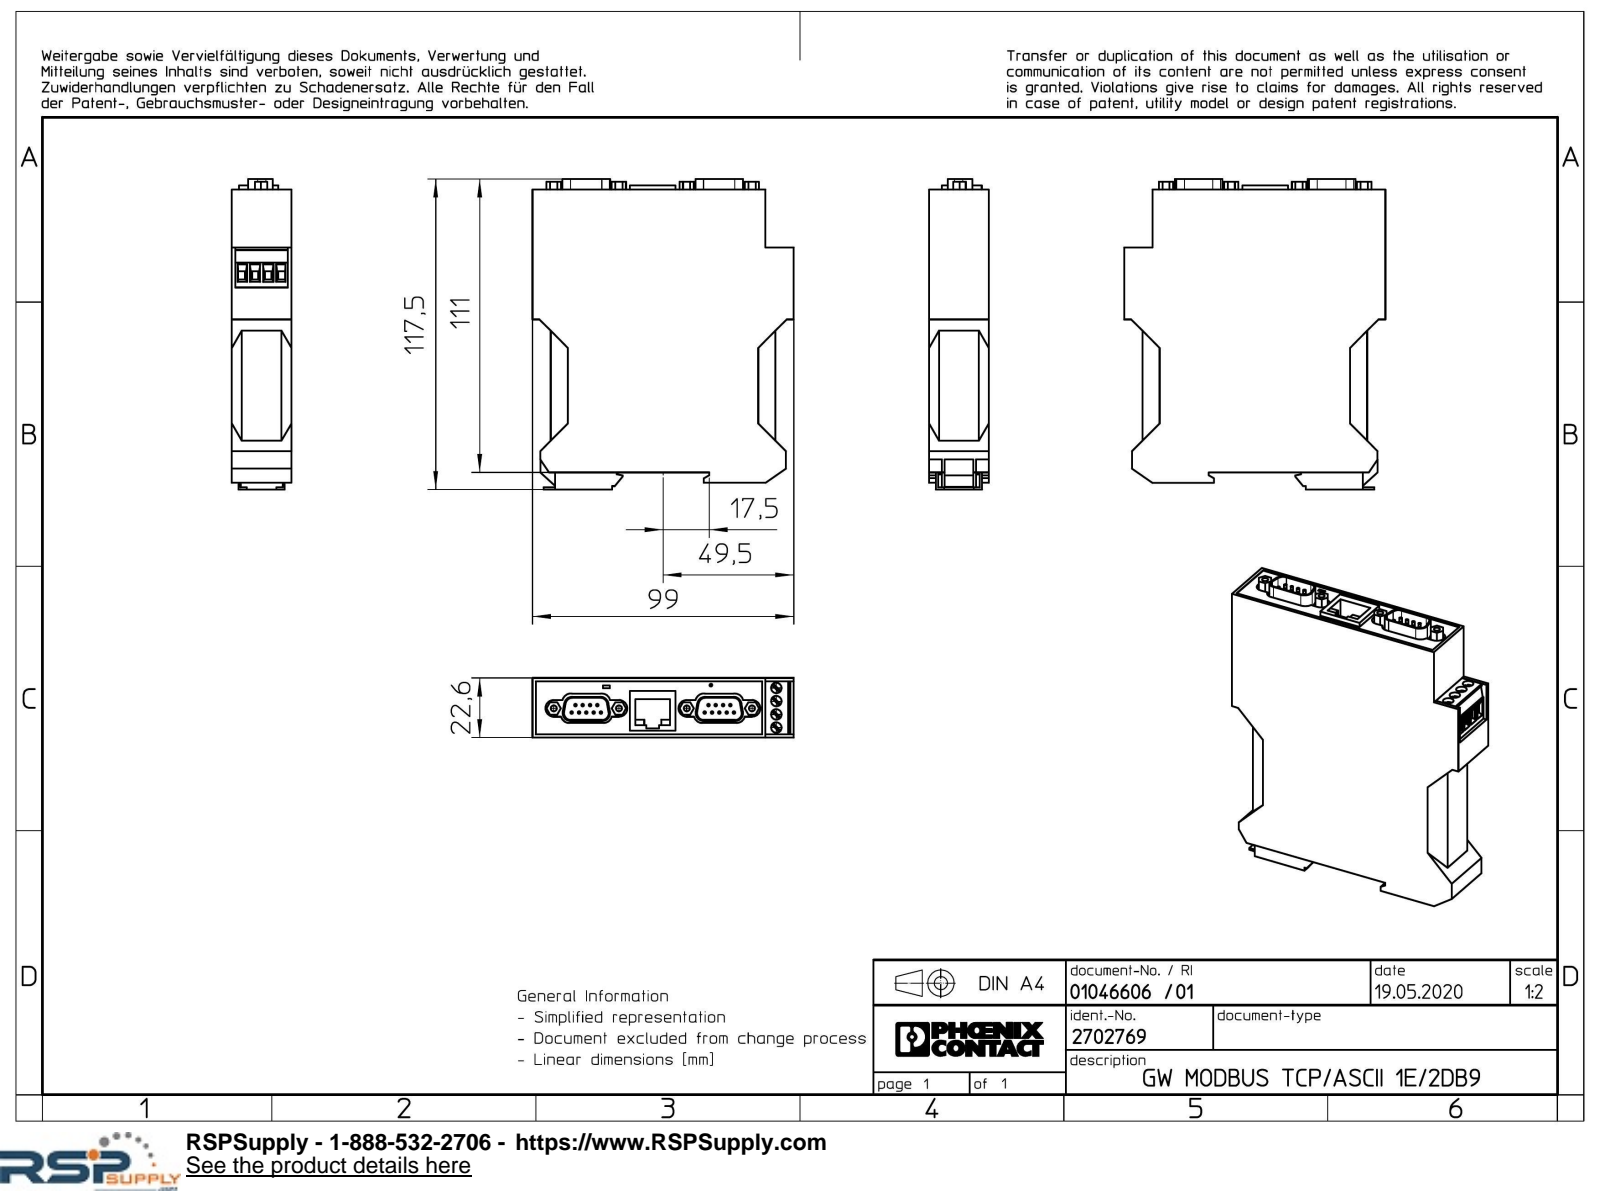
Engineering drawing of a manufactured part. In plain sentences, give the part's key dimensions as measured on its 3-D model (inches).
The part is named "GW_MODBUS_TCP_ASCII_1E_2DB9-select". Its 3-D file was written by "Creo Elements/Direct Modeling 20.1A 29-Sep-2018 (C) Parametric Technology GmbH (AUTOMOTIVE_DESIGN)". It is 1 solid with 362 faces: 280 planar, 82 cylindrical and 0 other. Overall it measures 4.626 by 3.898 by 0.89 inches. Its volume is 13.32 cubic inches and its surface area 50.88 square inches. Round holes: 4 of diameter 0.09, 4 of diameter 0.157, 1 of diameter 0.043. Round bosses or shafts: 18 of diameter 0.039. Partial cylindrical surfaces (rounded edges, fillets, slot ends): 12 of radius 0.125, 8 of radius 0.1, 8 of radius 0.12. The main face-to-face distances are 0.89, 0.157, 3.624, 0.274, 4.205, 4.362, 3.35, 3.476, 3.203, 0.148. The hole center spacings are 0.197, 0.394, 0.974, 1.984, 0.373, 0.378, 0.462, 0.473.
